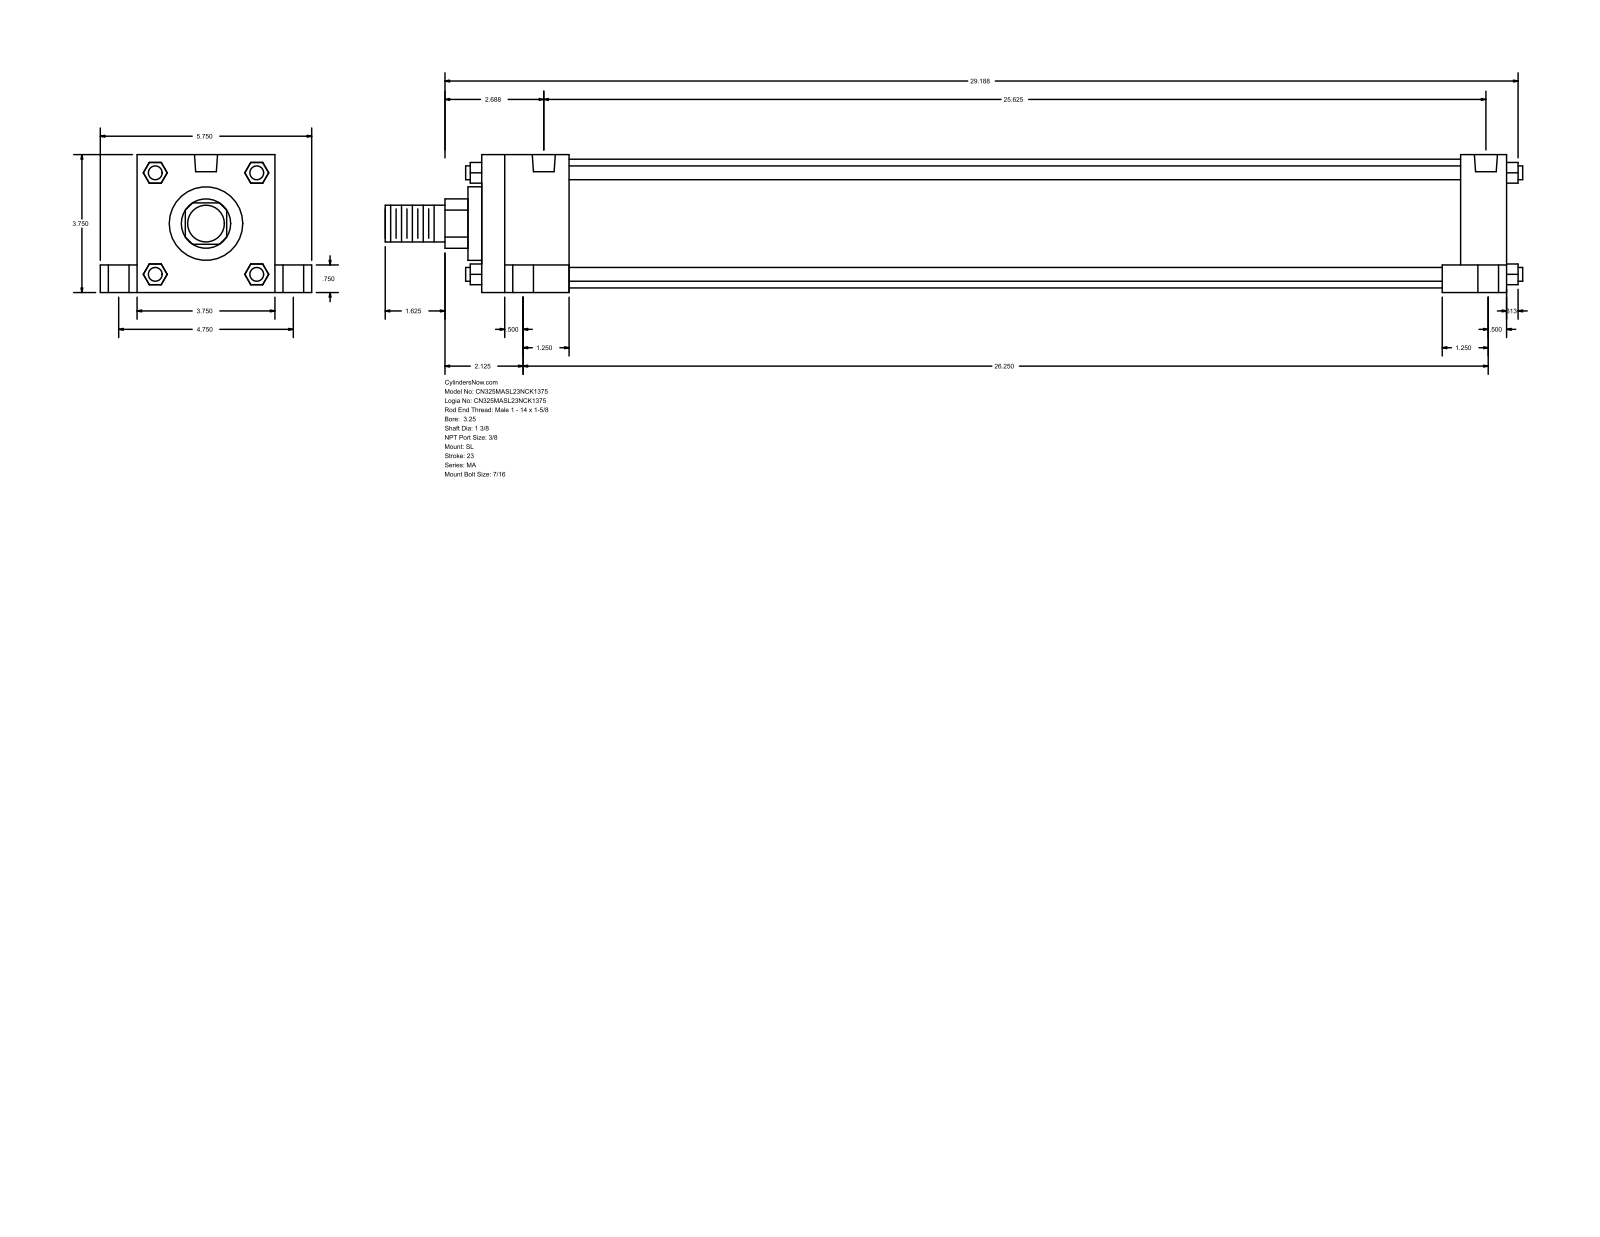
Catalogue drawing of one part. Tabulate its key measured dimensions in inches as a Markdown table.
| quantity | value |
| --- | --- |
| part name | MA_SL__0325_1.375 |
| STEP written by | GSSL Pune (CONFIG_CONTROL_DESIGN) |
| units | inches |
| bodies | 0 solids, 148 faces (112 planar, 36 cylindrical, 0 other) |
| overall size | 30.937 × 5.75 × 3.75 |
| round holes (diameter × count) | 0.437 × 4, 0.563 × 4, 0.813 × 4, 0.627 × 2 |
| round bosses / shafts (diameter × count) | 0.375 × 4, 3.5 × 1, 2 × 1, 1.375 × 1, 1 × 1 |
| partial cylindrical surfaces (radius × count) | 0.672 × 1 |
| main face-to-face distances | 3.75, 27.875, 24.25, 1, 4.75, 26.625, 1.25, 2.375, 25.5, 0.75 |
| hole center spacings | 2.376, 2.388, 2.441, 2.491, 4.75, 25.25, 25.61, 25.797 |
